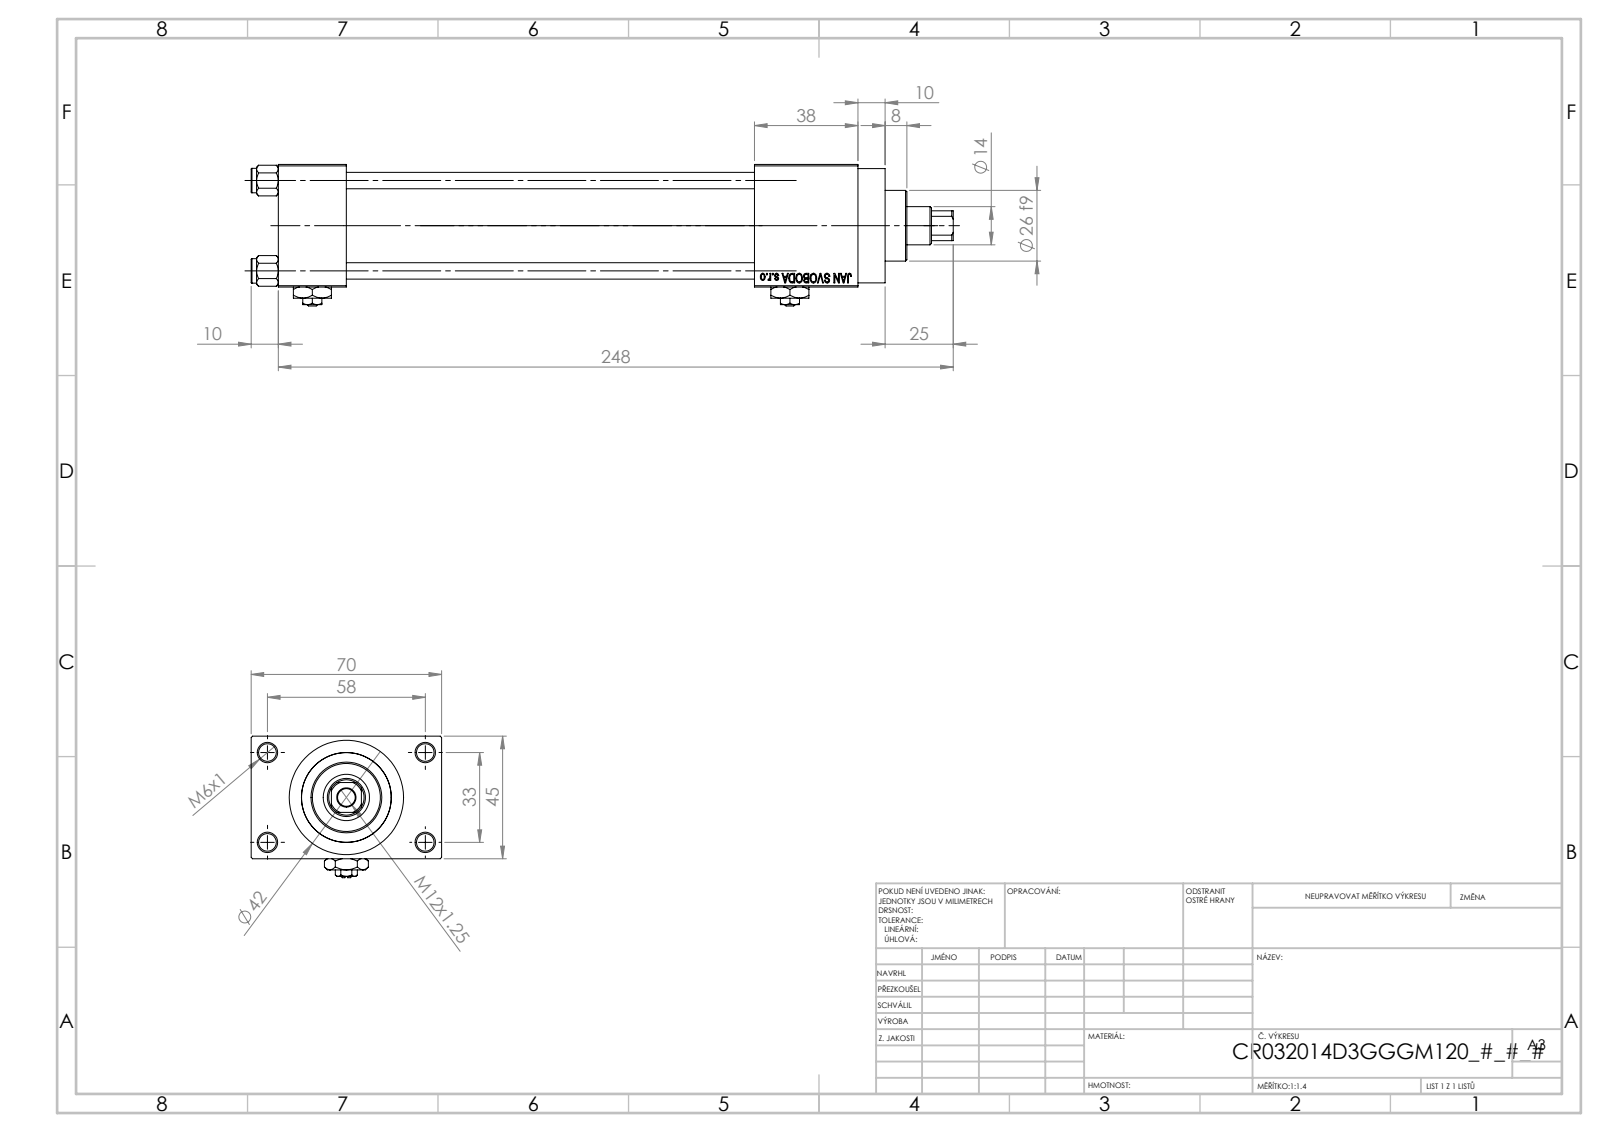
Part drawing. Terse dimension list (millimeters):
name: Zatka_pro_OIL_PORT; V215CR_D_Body; V215CR_D_TYCINKA; NUT_M5_D (+2 more)
written by: SolidWorks 2019 (CONFIG_CONTROL_DESIGN)
unit: mm
bodies: 13 solids, 1202 faces (542 planar, 100 cylindrical, 560 other)
size: 258 × 70 × 52
volume: 290 388 mm³; area: 110 546 mm²
holes: 5× ⌀6.5, 4× ⌀6, 2× ⌀7, 2× ⌀13.16, 2× ⌀20, 1× ⌀14, 1× ⌀17, 1× ⌀24, 1× ⌀32, 1× ⌀33
bosses: 4× ⌀9, 1× ⌀42, 1× ⌀38, 1× ⌀26
rounds: 1× R6.5
face distances: 45, 25, 12.5, 57.5, 150, 175, 188, 70, 38, 213
hole spacings: 12.4, 23.48, 33.2, 33.37, 35.35, 45.6, 56.35, 33
